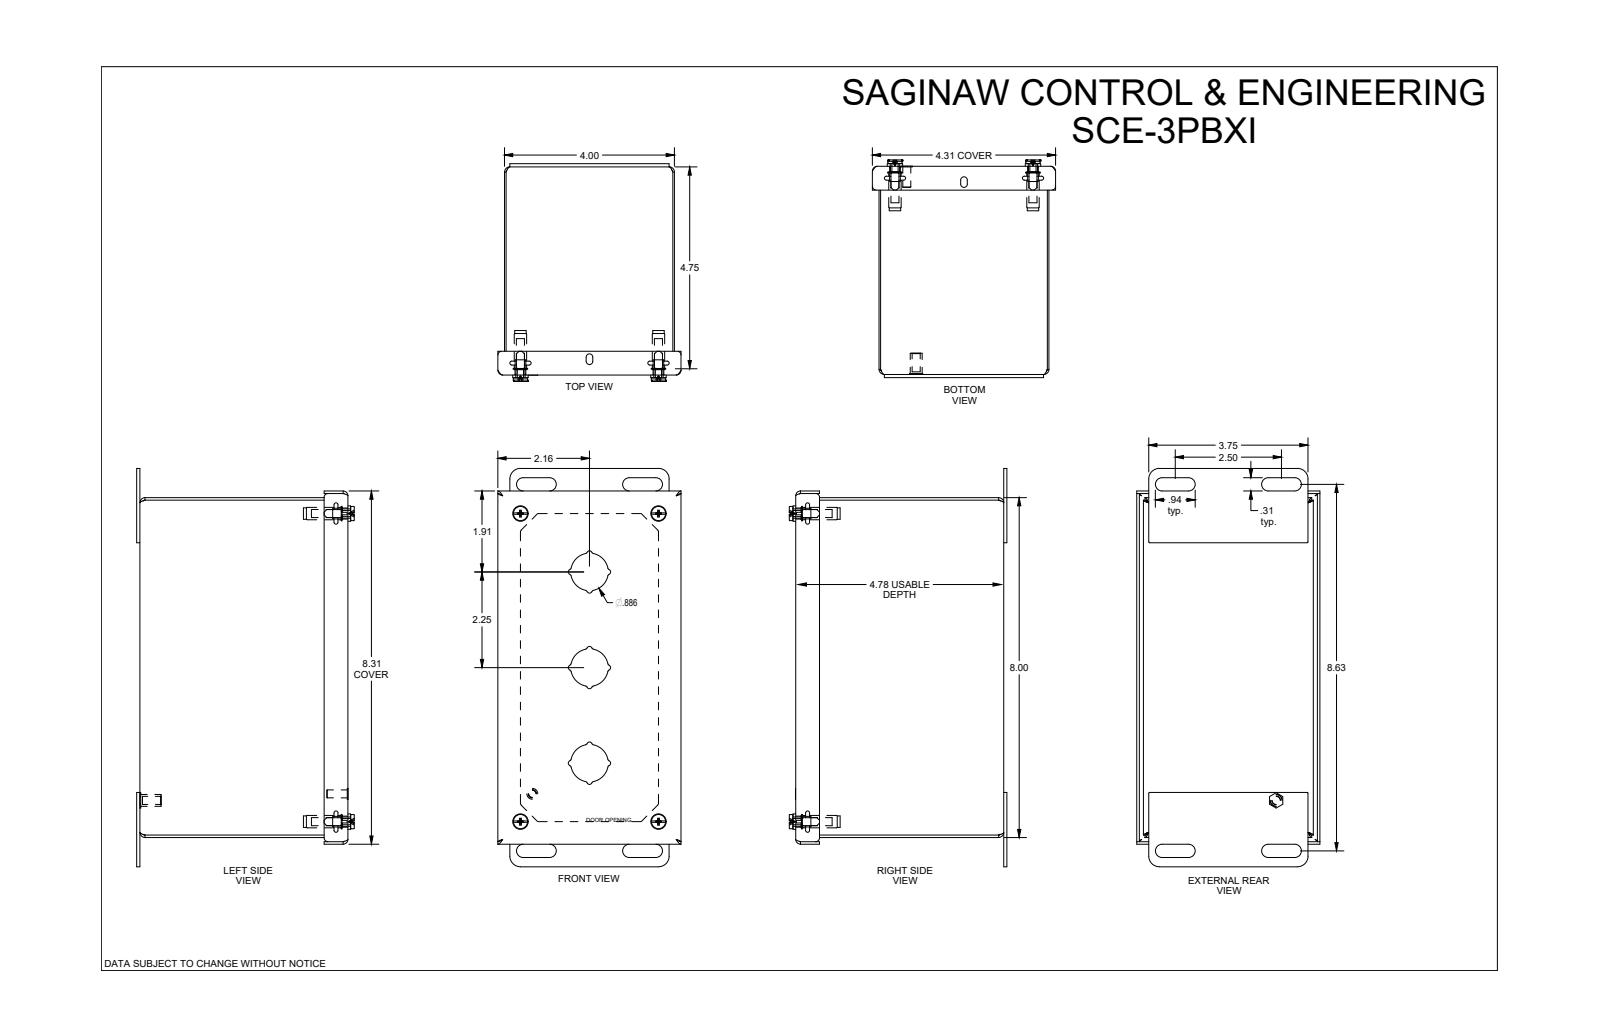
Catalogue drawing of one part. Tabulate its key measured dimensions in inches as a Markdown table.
| quantity | value |
| --- | --- |
| part name | SCE-3PBXI |
| STEP written by | SolidWorks 2021 (AUTOMOTIVE_DESIGN) |
| units | inches |
| bodies | 3 solids, 464 faces (153 planar, 227 cylindrical, 84 other) |
| overall size | 9.375 × 5.036 × 4.313 |
| volume | 13.33 in³ |
| surface area | 427.9 in² |
| round holes (diameter × count) | 0.19 × 5, 0.22 × 4, 0.25 × 4, 0.266 × 4, 0.317 × 4 |
| round bosses / shafts (diameter × count) | 0.362 × 4, 0.34 × 4, 0.292 × 4, 0.27 × 4, 0.26 × 4, 0.28 × 1, 0.256 × 1, 0.188 × 1 |
| partial cylindrical surfaces (radius × count) | 0.04 × 24, 0.06 × 20, 0.062 × 12, 0.015 × 8, 0.115 × 8, 0.156 × 8, 0.245 × 8, 0.02 × 4 |
| main face-to-face distances | 0.06, 3.94, 4.838, 4, 3.88, 7.94, 4.778, 4.898, 0.156, 8 |
| hole center spacings | 7.945, 3.25, 7.25, 0.707, 3.25, 3.25, 7.25, 7.25 |
